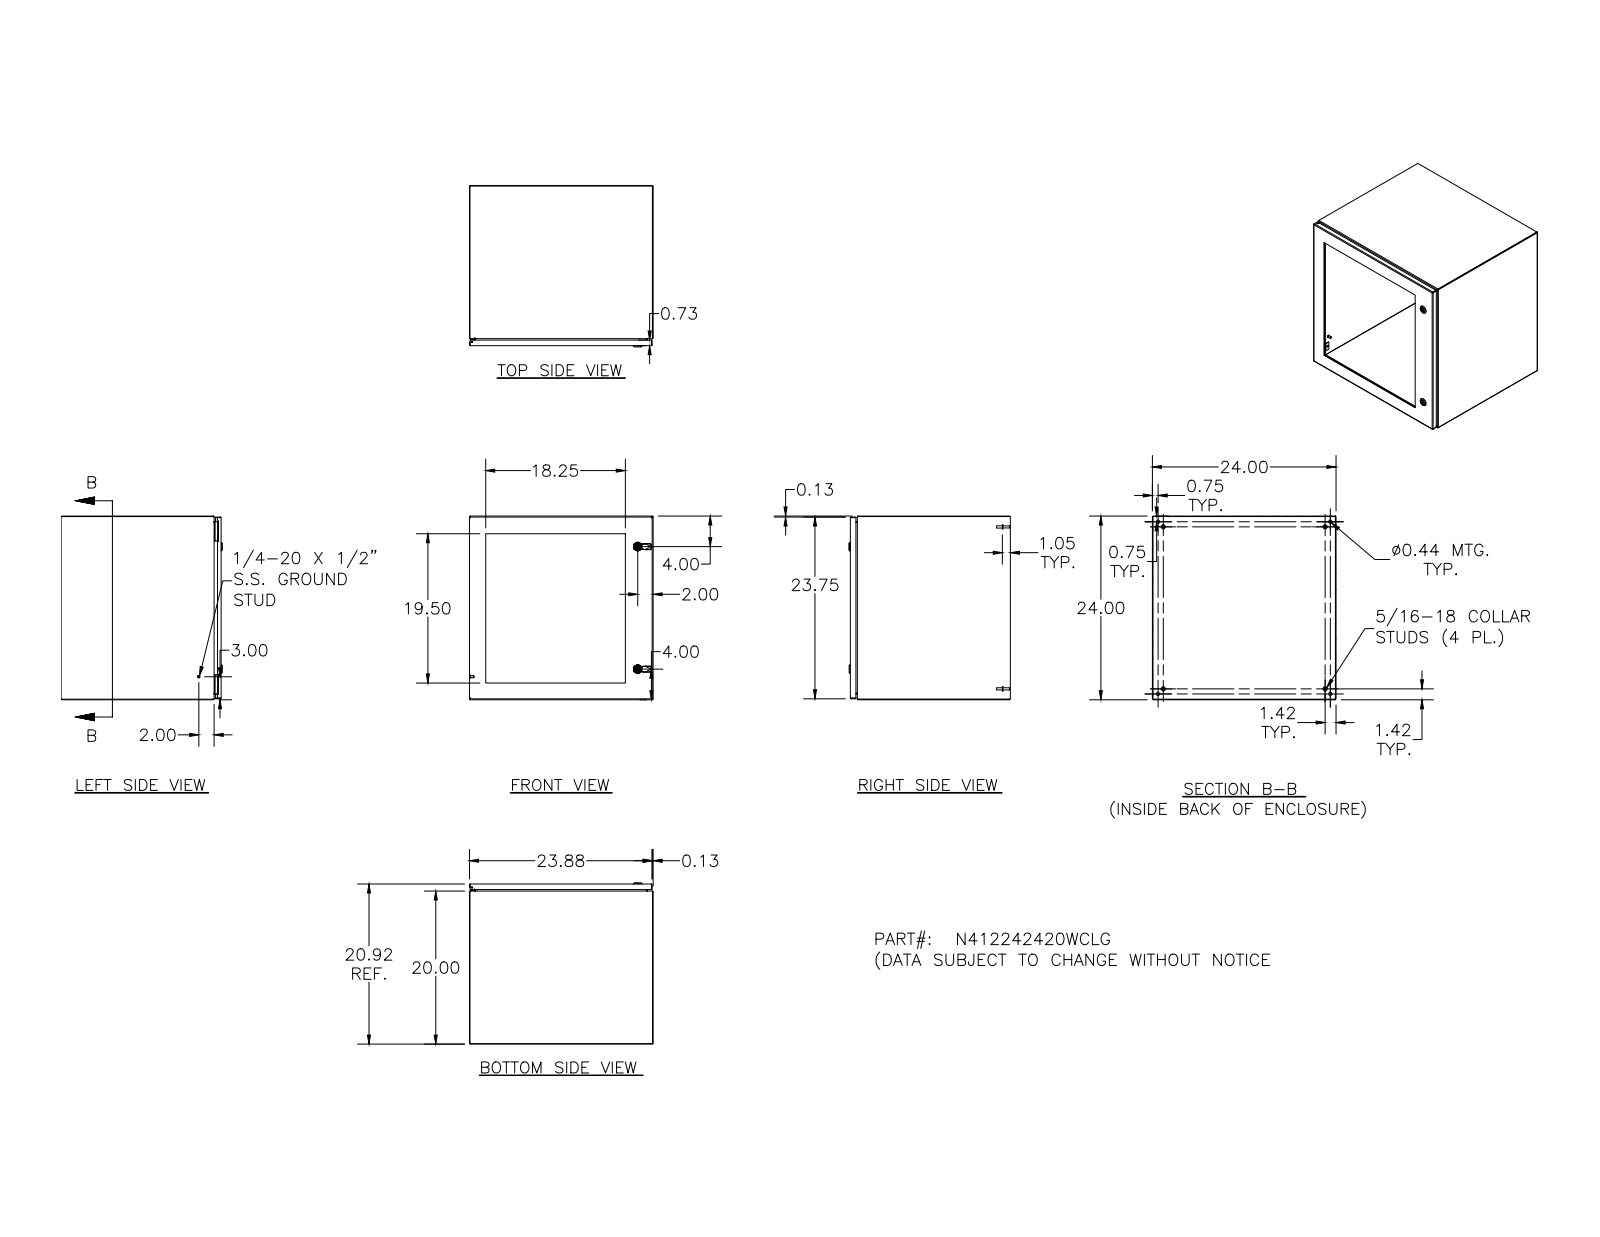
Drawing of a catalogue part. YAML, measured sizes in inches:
part_name: "N412242420WCLG"
step_written_by: "SolidWorks 2018 (AUTOMOTIVE_DESIGN)"
units: inches
bodies: {solids: 86, faces: 2484, planar: 969, cylindrical: 746, other: 769}
overall_size: [24, 24, 21.075]
volume: 320.5
surface_area: 6857
round_holes:
  - {diameter: 0.156, count: 22}
  - {diameter: 0.281, count: 20}
  - {diameter: 0.188, count: 5}
  - {diameter: 0.093, count: 4}
  - {diameter: 0.152, count: 4}
  - {diameter: 0.167, count: 4}
  - {diameter: 0.172, count: 4}
  - {diameter: 0.438, count: 4}
  - {diameter: 0.197, count: 2}
  - {diameter: 0.315, count: 2}
  - {diameter: 0.394, count: 2}
  - {diameter: 0.402, count: 2}
round_bosses_or_shafts:
  - {diameter: 0.337, count: 20}
  - {diameter: 0.19, count: 20}
  - {diameter: 0.25, count: 10}
  - {diameter: 0.563, count: 4}
  - {diameter: 0.36, count: 4}
  - {diameter: 0.32, count: 4}
  - {diameter: 0.3, count: 4}
  - {diameter: 0.256, count: 4}
partial_cylinders:
  - {radius: 0.012, count: 54}
  - {radius: 0.031, count: 33}
  - {radius: 0.05, count: 26}
  - {radius: 0.02, count: 23}
  - {radius: 0.105, count: 22}
  - {radius: 0.016, count: 18}
  - {radius: 0.125, count: 16}
  - {radius: 0.032, count: 8}
face_to_face_distances: [0.074, 23.926, 23.852, 24, 20.843, 20.769, 0.25, 20.593, 20.519, 20.917]
hole_center_spacings: [4, 8, 21.132, 12, 20, 22.239, 20.75, 6.221]
